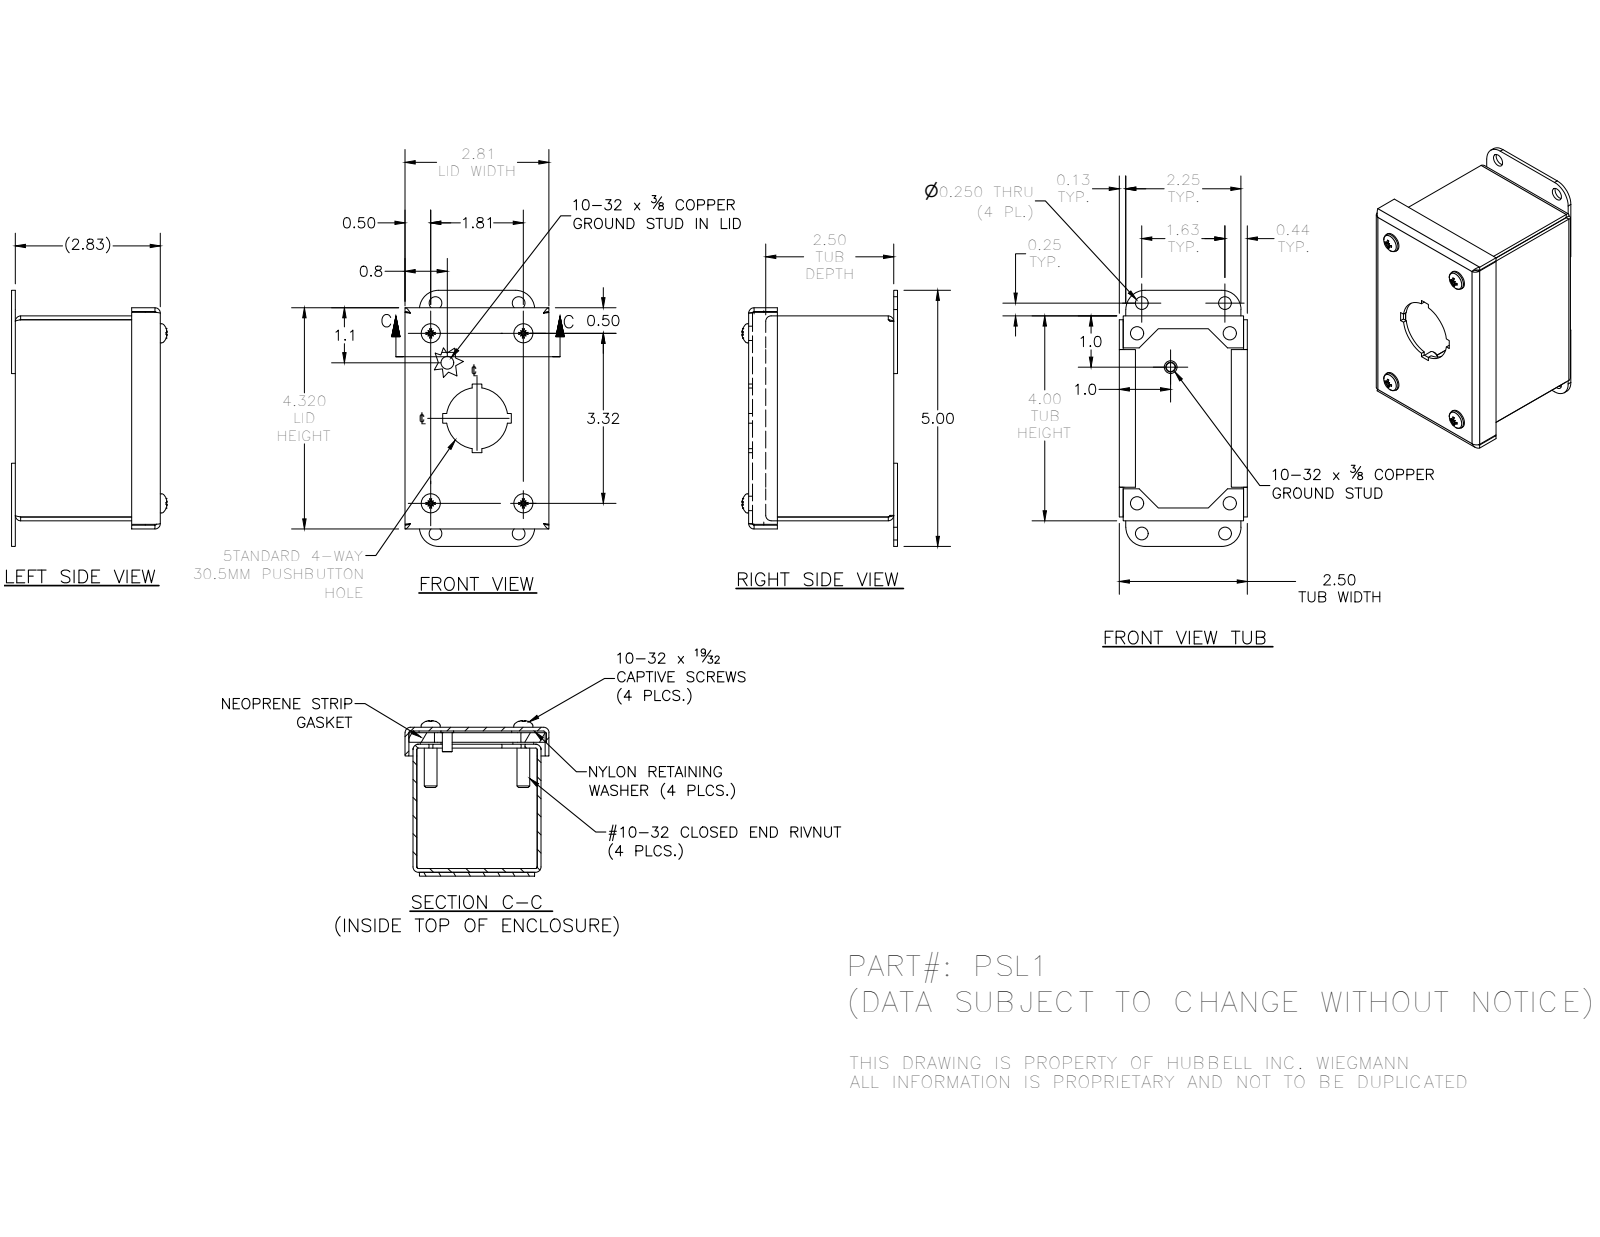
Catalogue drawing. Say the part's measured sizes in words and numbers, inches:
The part is named "PSL1LID; 372163; 39077; PSL1BKP (+5 more)". Its 3-D file was written by "Autodesk Inventor 2016 (AUTOMOTIVE_DESIGN)". It is 19 solids with 498 faces: 276 planar, 108 cylindrical and 114 other. Overall it measures 5 by 3.036 by 2.81 inches. Its volume is 6.387 cubic inches and its surface area 166 square inches. Round holes: 4 of diameter 0.156, 4 of diameter 0.196, 4 of diameter 0.25, 4 of diameter 0.257, 4 of diameter 0.278, 4 of diameter 0.281, 4 of diameter 0.313, 1 of diameter 1.2. Round bosses or shafts: 6 of diameter 0.19, 4 of diameter 0.453, 4 of diameter 0.406, 4 of diameter 0.373, 4 of diameter 0.248, 2 of diameter 0.25. Partial cylindrical surfaces (rounded edges, fillets, slot ends): 12 of radius 0.031, 12 of radius 0.105, 8 of radius 0.063, 4 of radius 0.089, 4 of radius 0.375. The main face-to-face distances are 0.074, 2.426, 2.758, 2.832, 2.5, 2.352, 3.926, 2.684, 0.106, 0.188. The hole center spacings are 1.891, 3.781, 4.271, 0.597, 0.597, 1.81, 1.816, 1.824.
